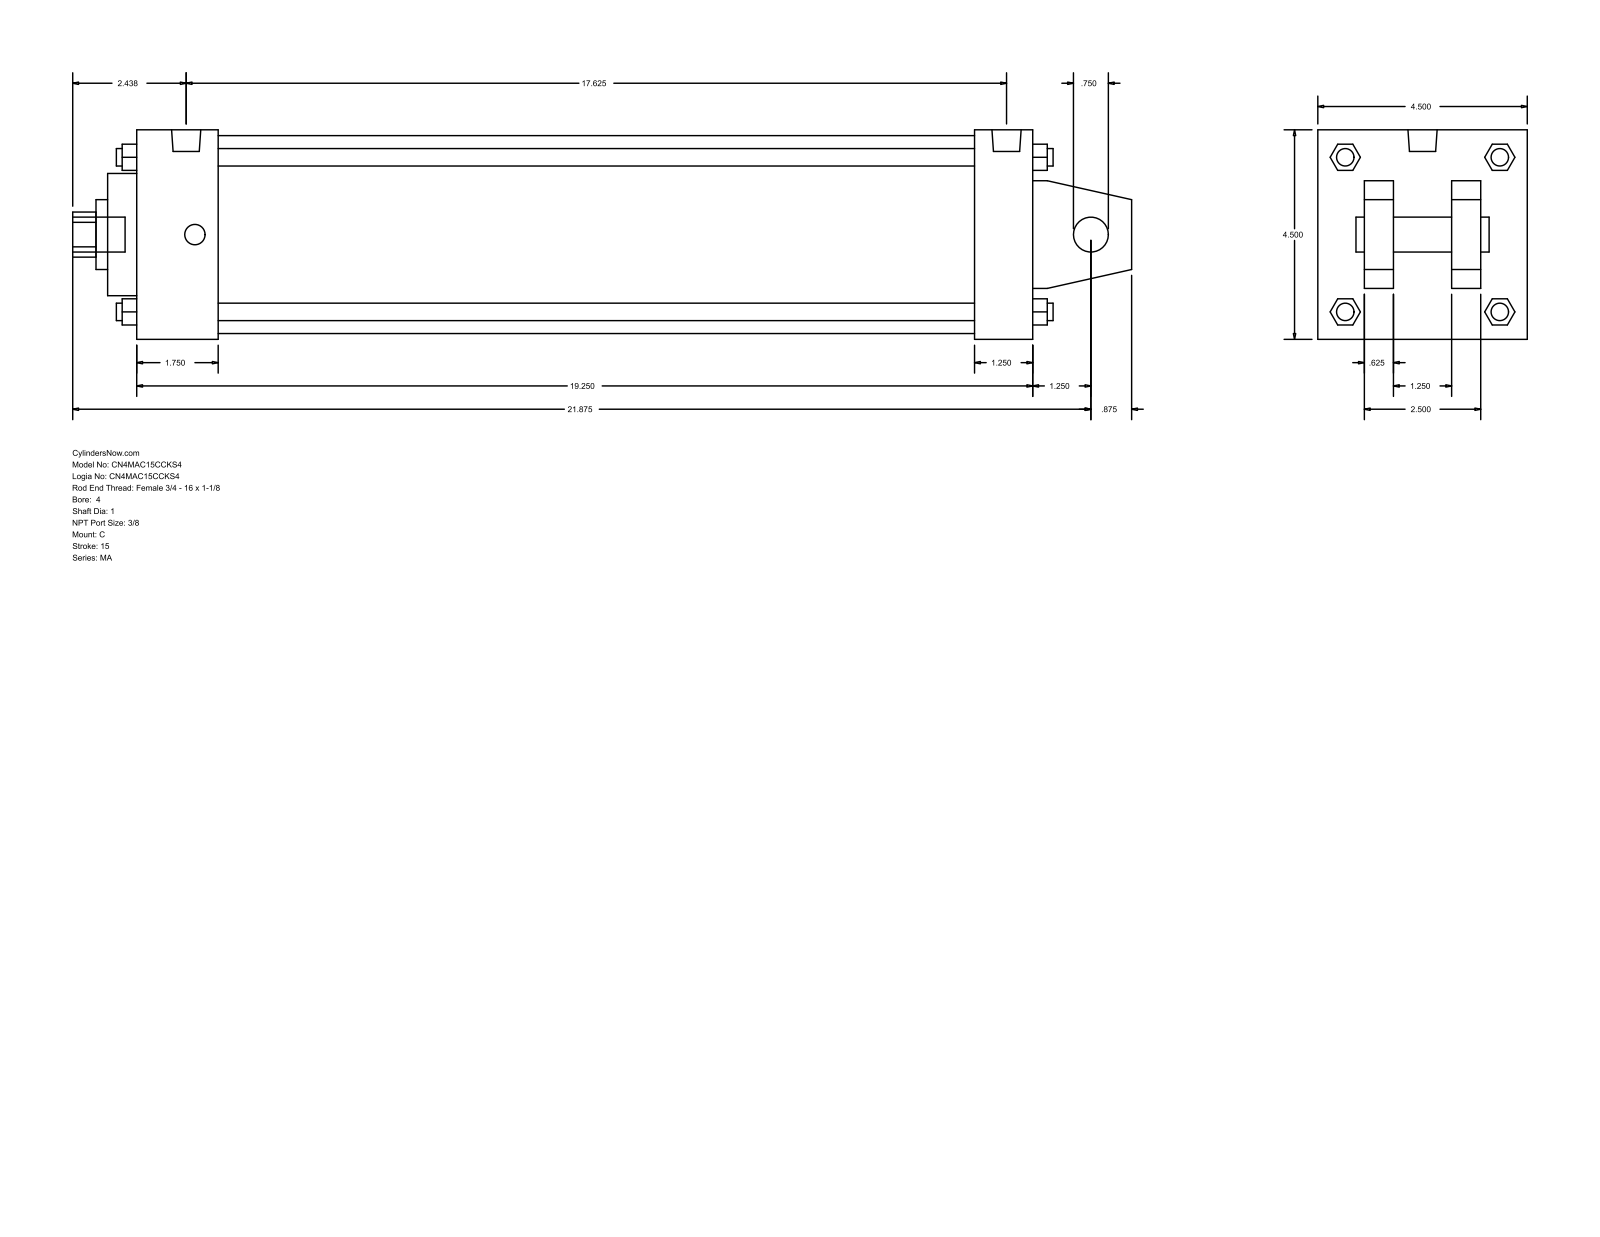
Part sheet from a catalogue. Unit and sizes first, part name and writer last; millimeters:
Units: millimetres
Overall size (bounding box): 577.85 × 114.3 × 114.3
Round holes (diameter × count): ⌀19.05 ×1, ⌀25.4 ×1, ⌀38.1 ×1, ⌀66.67 ×1, ⌀107.95 ×1
Round bosses / shafts (diameter × count): ⌀11.11 ×4, ⌀9.53 ×4, ⌀15.93 ×2, ⌀19.05 ×1
Partial cylindrical surfaces — rounded edges, fillets, slot ends (radius × count): R12.29 ×1
Main face-to-face distances: 114.3, 488.96, 15.87, 31.76, 73.03, 41.27, 25.4, 88.9, 47.63, 457.2
Bodies: 0 solids, 141 faces (109 planar, 32 cylindrical, 0 other)
Part name (STEP PRODUCT): MA_C__0400_1
STEP written by: GSSL Pune (CONFIG_CONTROL_DESIGN)
